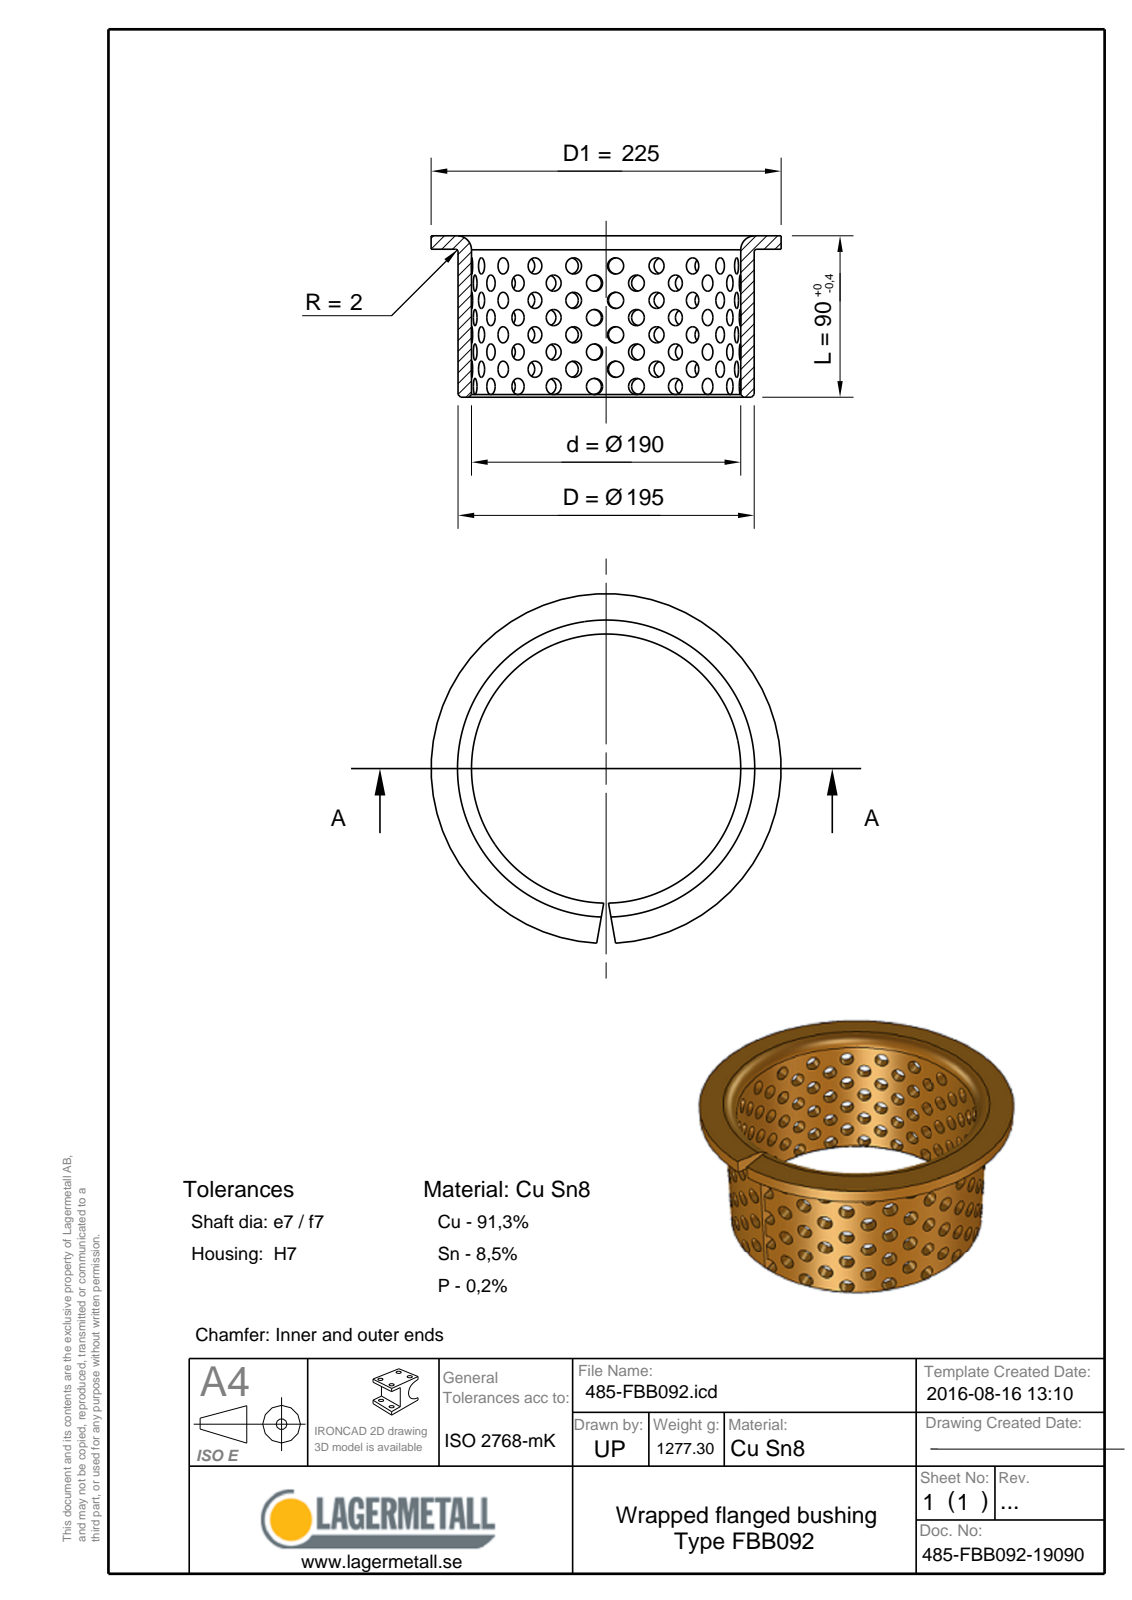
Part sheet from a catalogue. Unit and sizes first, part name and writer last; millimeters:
Units: millimetres
Overall size (bounding box): 225 × 224.94 × 90
Round holes (diameter × count): ⌀190 ×1
Round bosses / shafts (diameter × count): ⌀225 ×1, ⌀195 ×1
Main face-to-face distances: 2.5, 87.5, 90
Volume: 157 691 mm³ · Surface area: 129 765 mm²
Bodies: 1 solid, 12 faces (5 planar, 3 cylindrical, 4 other)
Part name (STEP PRODUCT): 485-FBB092-19090
STEP written by: Spatial InterOp 3D (CONFIG_CONTROL_DESIGN)
